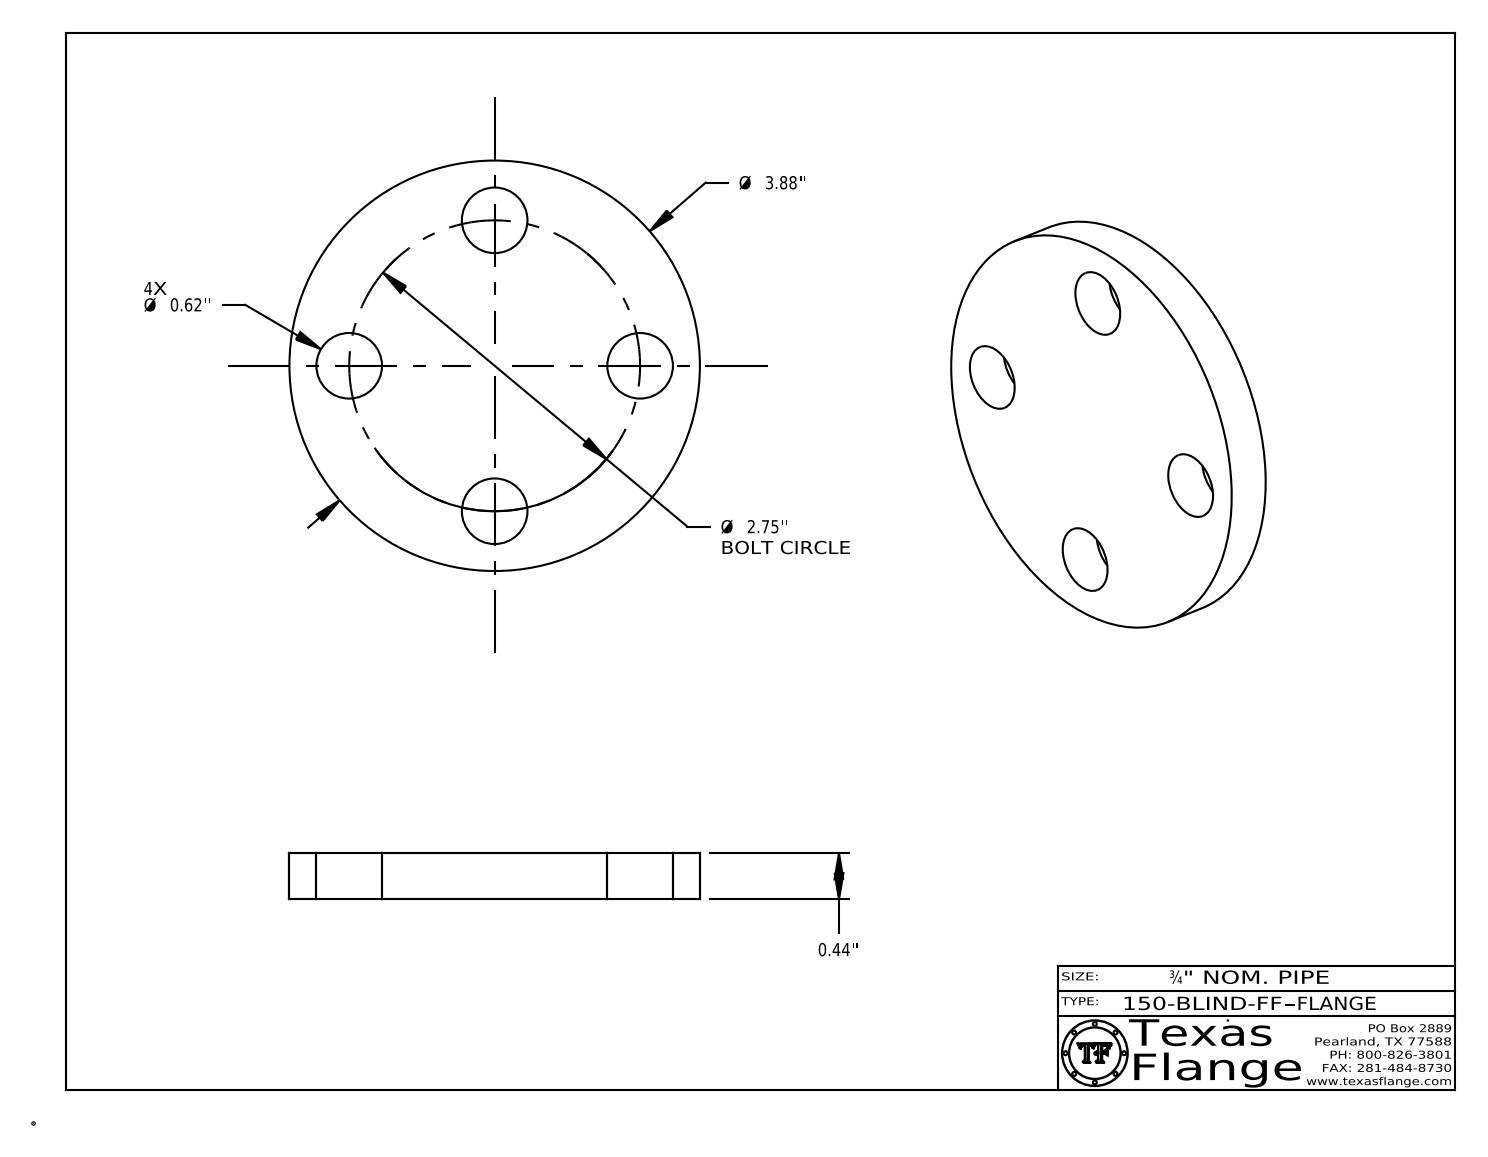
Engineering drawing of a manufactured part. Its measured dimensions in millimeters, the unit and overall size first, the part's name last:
Units: millimetres
Overall size (bounding box): 98.6 × 98.6 × 11.2
Round holes (diameter × count): ⌀15.7 ×4, ⌀12.6 ×1
Round bosses / shafts (diameter × count): ⌀0.8 ×8, ⌀98.6 ×1, ⌀9.9 ×1
Main face-to-face distances: 11.2, 10.8, 0.4, 3.8, 3.7, 0.7, 3.1, 2.4, 0.5, 2.6
Hole centre spacings: 49.4, 26.7, 64.5, 69.9
Volume: 76 530 mm³ · Surface area: 19 430 mm²
Bodies: 1 solid, 397 faces (367 planar, 30 cylindrical, 0 other)
Part name (STEP PRODUCT): 150-BLIND-FF
STEP written by: CATIA V5 STEP AP214 (AUTOMOTIVE_DESIGN)
